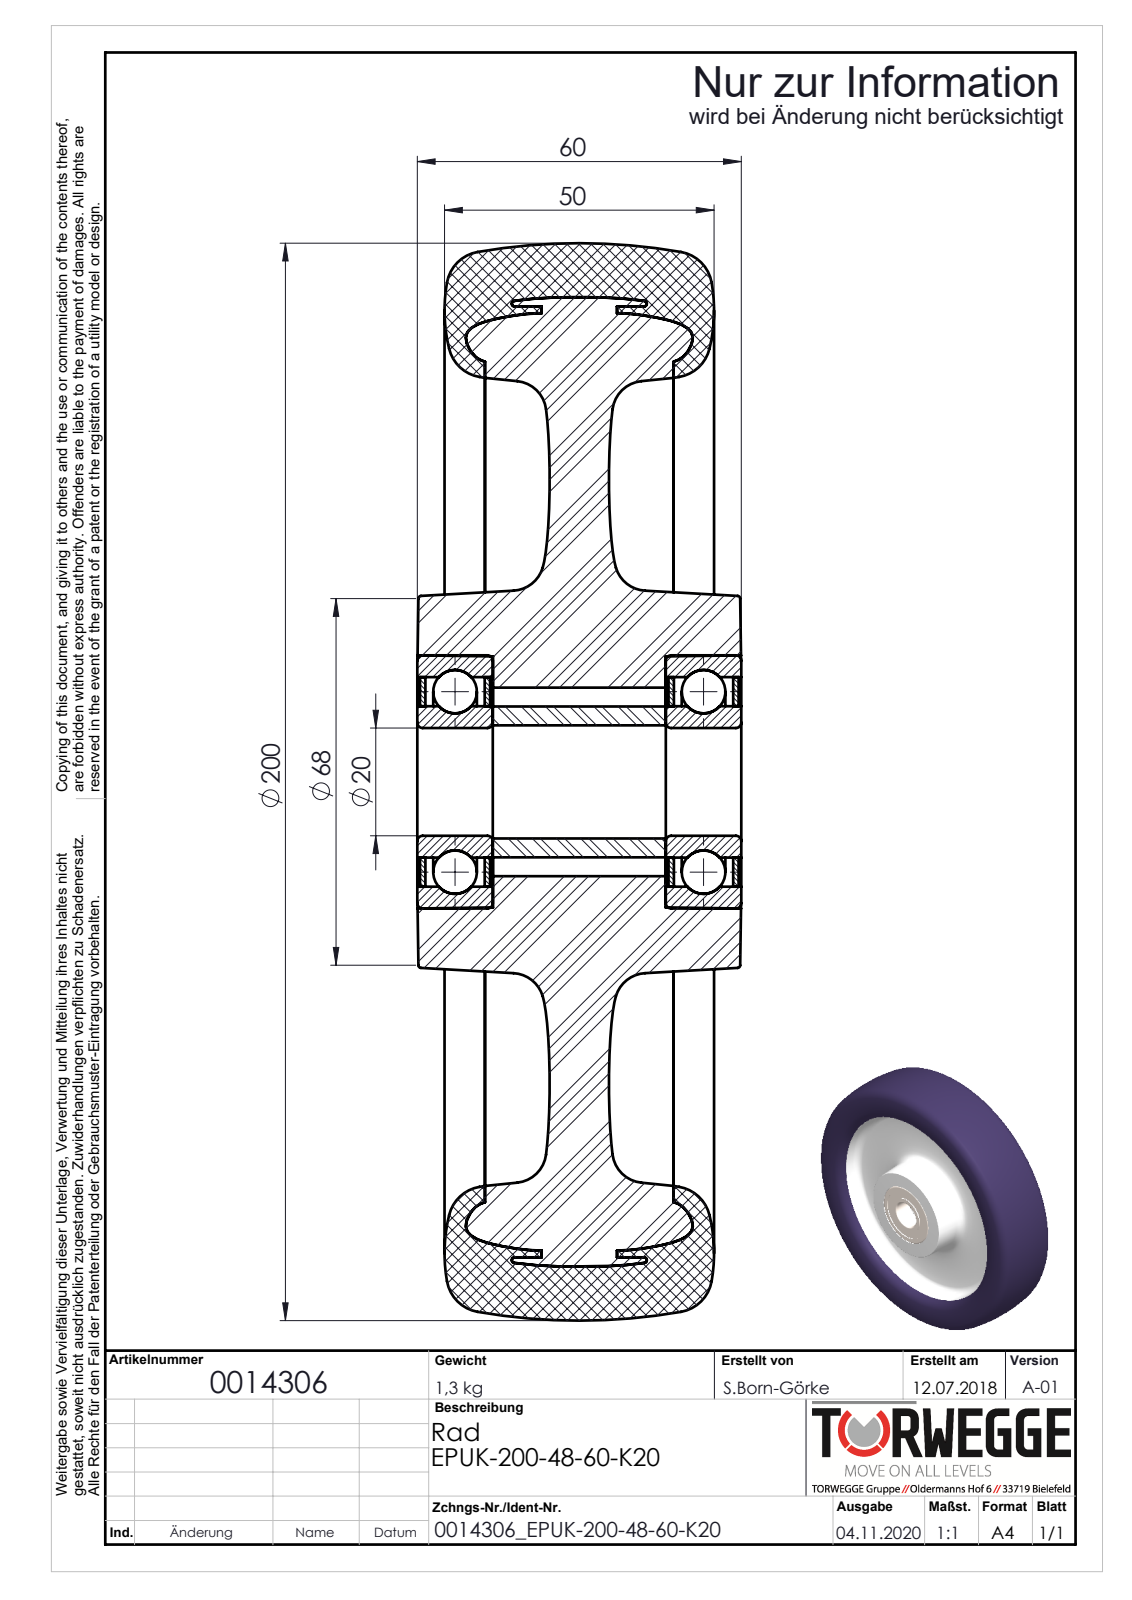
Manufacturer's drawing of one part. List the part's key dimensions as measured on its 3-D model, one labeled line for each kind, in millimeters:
Part name (STEP PRODUCT): 0014306
STEP written by: SolidWorks 2018 (AUTOMOTIVE_DESIGN)
Units: millimetres
Bodies: 12 solids, 208 faces (52 planar, 50 cylindrical, 106 other)
Overall size (bounding box): 200 × 198.37 × 60.1
Volume: 1 005 000 mm³ · Surface area: 146 101 mm²
Round holes (diameter × count): ⌀20 ×1, ⌀21 ×1, ⌀28.1 ×1, ⌀35 ×1, ⌀38.9 ×1
Round bosses / shafts (diameter × count): ⌀47 ×1, ⌀28 ×1
Partial cylindrical surfaces — rounded edges, fillets, slot ends (radius × count): R87 ×1
Main face-to-face distances: 46.1, 0.5, 1.5, 12.5, 13.5, 1, 12, 32.05, 14, 14.05
